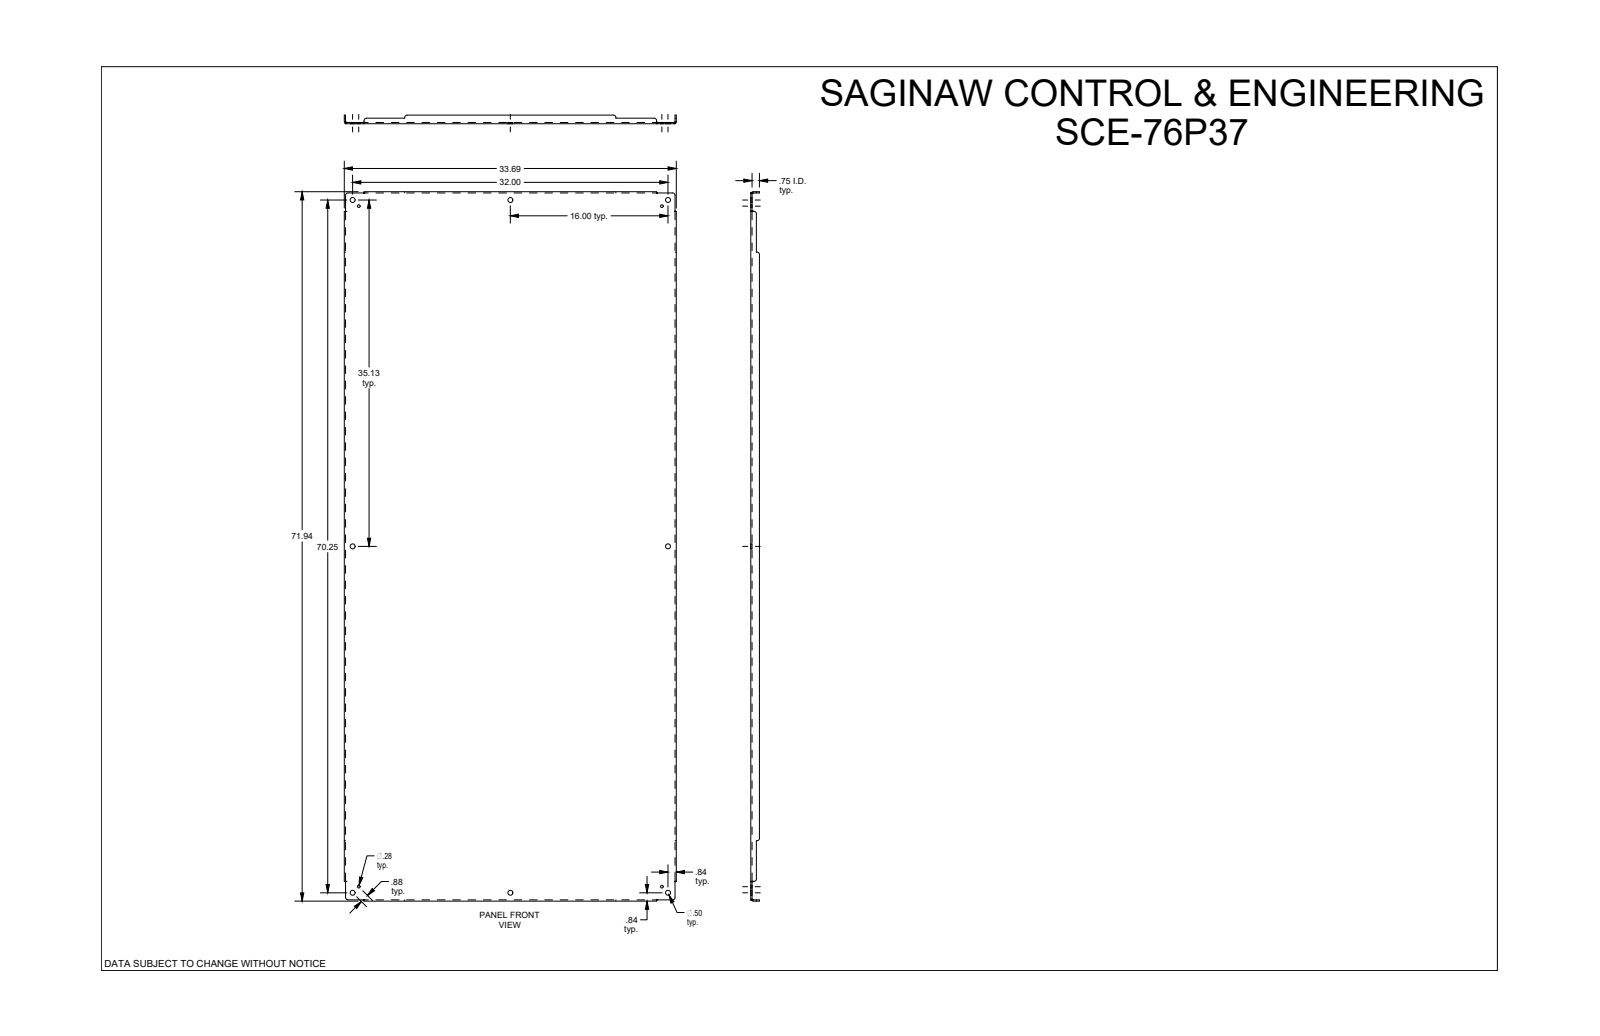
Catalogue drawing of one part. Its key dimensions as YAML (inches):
part_name: "SCE-76P37"
step_written_by: "SolidWorks 2019 (CONFIG_CONTROL_DESIGN)"
units: inches
bodies: {solids: 1, faces: 110, planar: 46, cylindrical: 40, other: 24}
overall_size: [71.938, 33.688, 0.875]
volume: 317.6
surface_area: 5111
round_holes:
  - {diameter: 0.5, count: 8}
  - {diameter: 0.281, count: 4}
partial_cylinders:
  - {radius: 0.25, count: 12}
  - {radius: 0.112, count: 4}
  - {radius: 0.237, count: 4}
face_to_face_distances: [0.125, 33.563, 33.438, 33.687, 0.125, 71.813, 0.75, 0.875, 71.687, 71.938]
hole_center_spacings: [0.875, 15.394, 16, 31.387, 34.512, 35.125, 38.597, 46.642]
